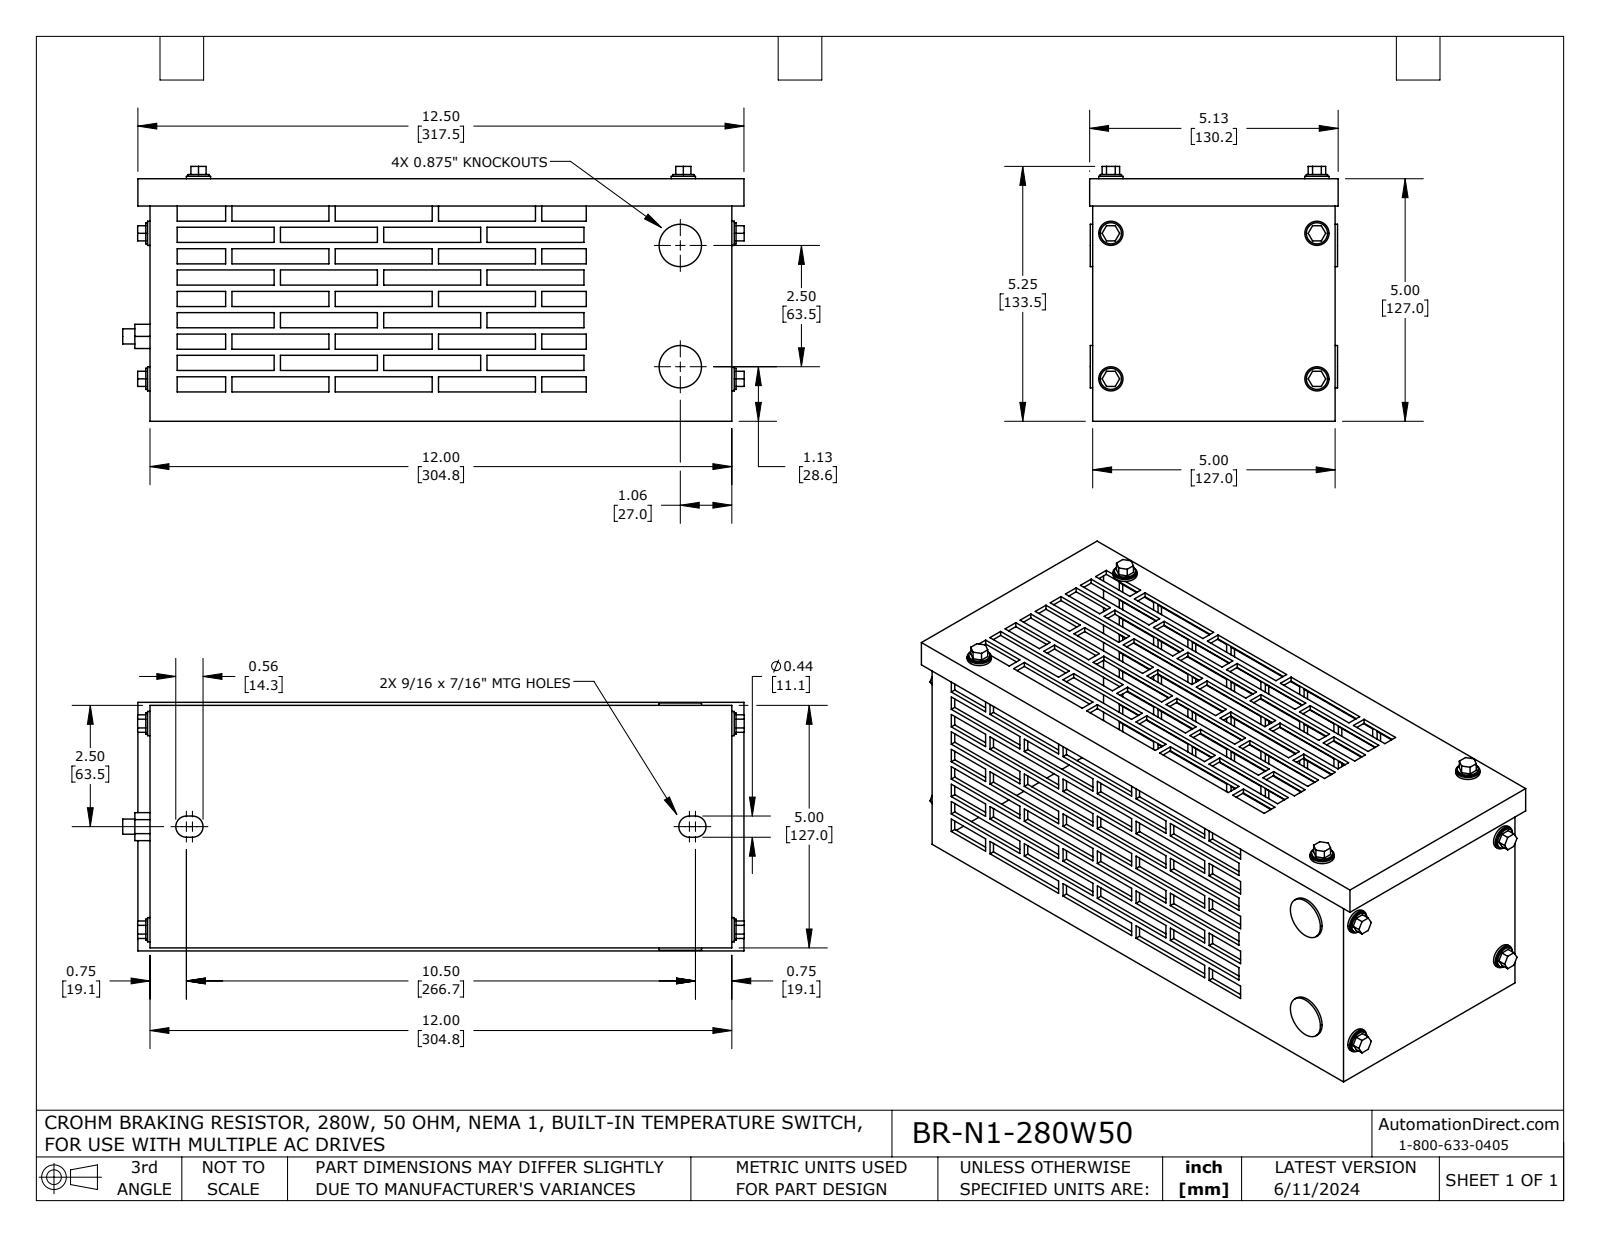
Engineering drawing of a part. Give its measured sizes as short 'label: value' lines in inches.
name: BR-N1-280W50
written by: SolidWorks 2021 (AUTOMOTIVE_DESIGN)
unit: in
bodies: 30 solids, 753 faces (659 planar, 94 cylindrical, 0 other)
size: 12.817 × 5.254 × 5.125
volume: 22.6 in³; area: 511.7 in²
holes: 8× ⌀0.25, 2× ⌀0.75
bosses: 8× ⌀0.5, 8× ⌀0.437, 2× ⌀0.875, 1× ⌀0.313
rounds: 4× R0.219
face distances: 0.1, 4.9, 5, 4.8, 11.9, 0.063, 4.963, 12, 11.8, 0.88
hole spacings: 4.25, 3, 5.202, 10, 10.865, 2.5
